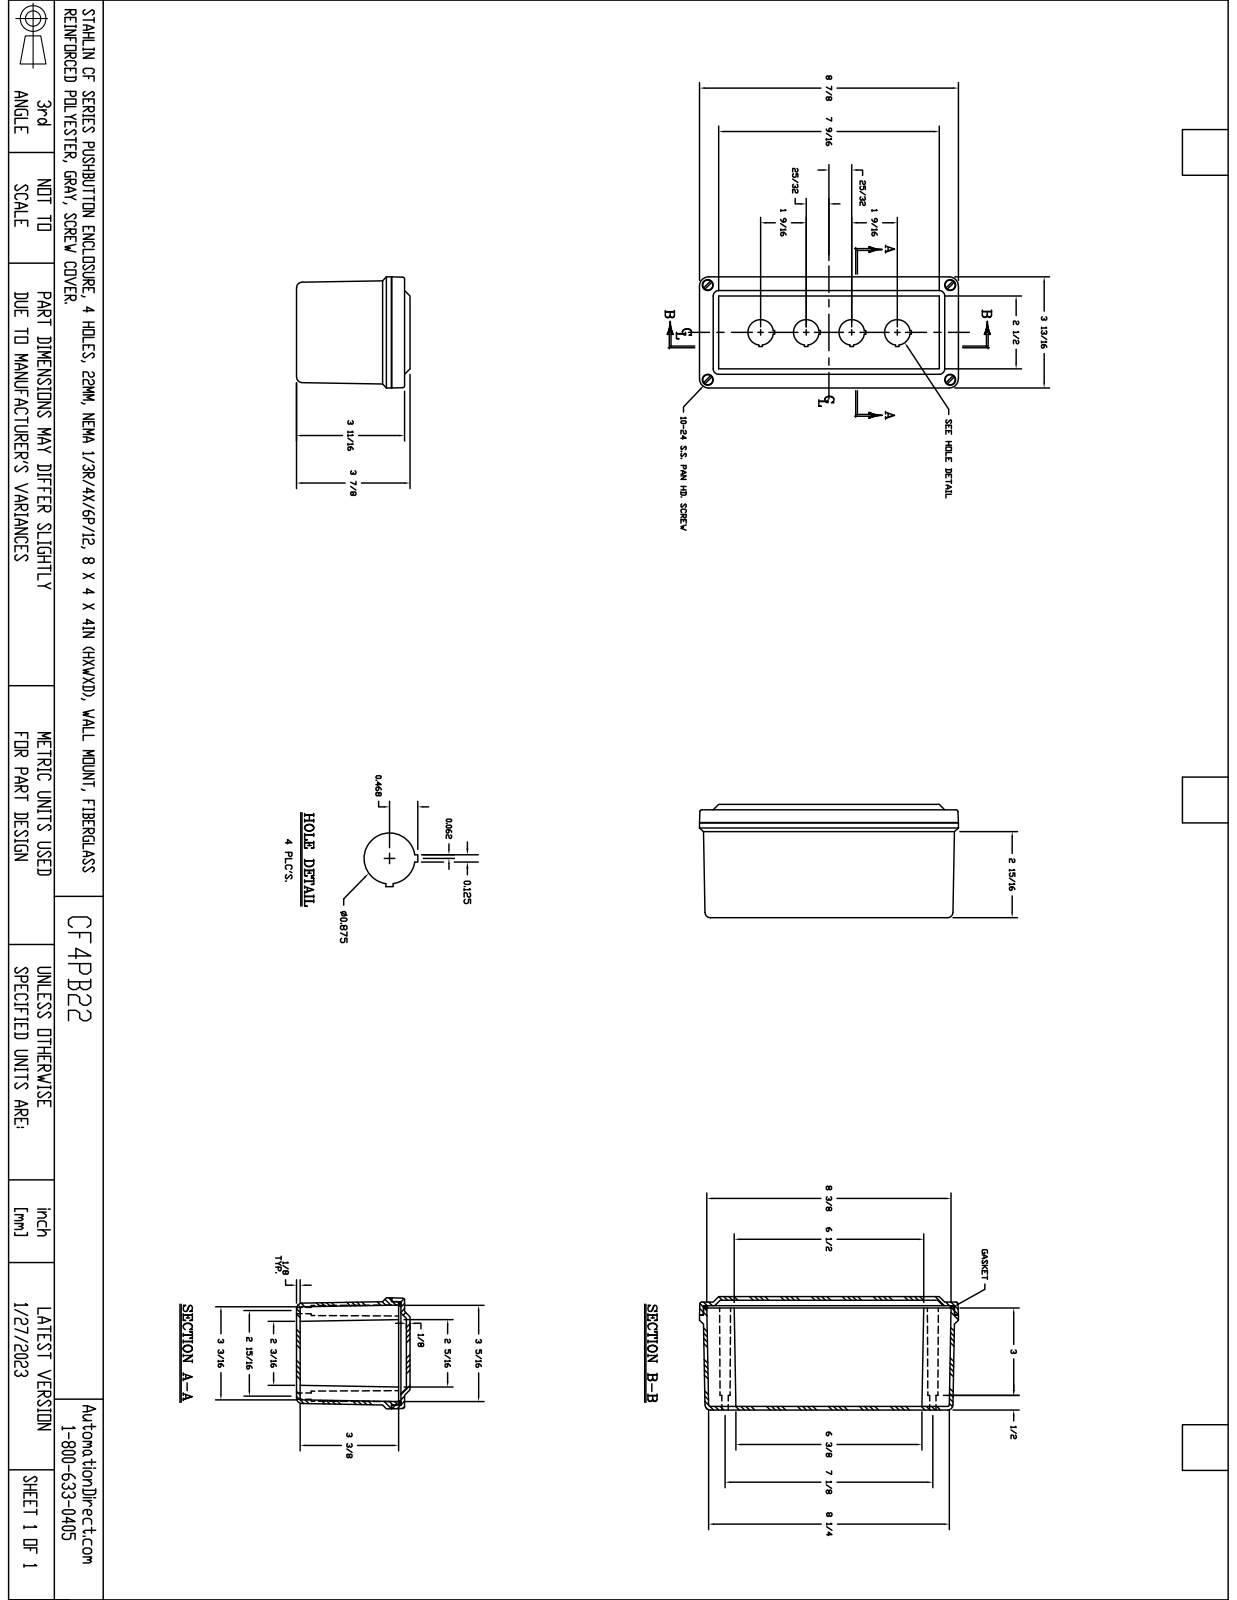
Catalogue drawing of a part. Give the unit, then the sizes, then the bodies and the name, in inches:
Units: inches
Overall size (bounding box): 11.125 × 3.875 × 3.813
Round holes (diameter × count): ⌀0.219 ×8, ⌀0.159 ×4, ⌀0.19 ×4, ⌀0.375 ×4, ⌀0.875 ×2
Round bosses / shafts (diameter × count): ⌀0.371 ×4, ⌀0.27 ×4, ⌀0.177 ×4
Partial cylindrical surfaces — rounded edges, fillets, slot ends (radius × count): R0.031 ×20, R0.012 ×16, R0.063 ×4, R0.176 ×4, R0.188 ×4, R0.22 ×4, R0.312 ×4, R0.325 ×4
Main face-to-face distances: 0.125, 0.131, 3.75, 0.187, 3.875, 3.625, 3.563, 0.5, 0.063, 3.687
Hole centre spacings: 0.614, 9.97, 10.562, 3.15, 10.437, 11.051, 7.796, 2.766
Volume: 28.79 in³ · Surface area: 403.1 in²
Bodies: 11 solids, 411 faces (207 planar, 108 cylindrical, 96 other)
Part name (STEP PRODUCT): CO4PB22
STEP written by: SolidWorks 2018 (AUTOMOTIVE_DESIGN)
